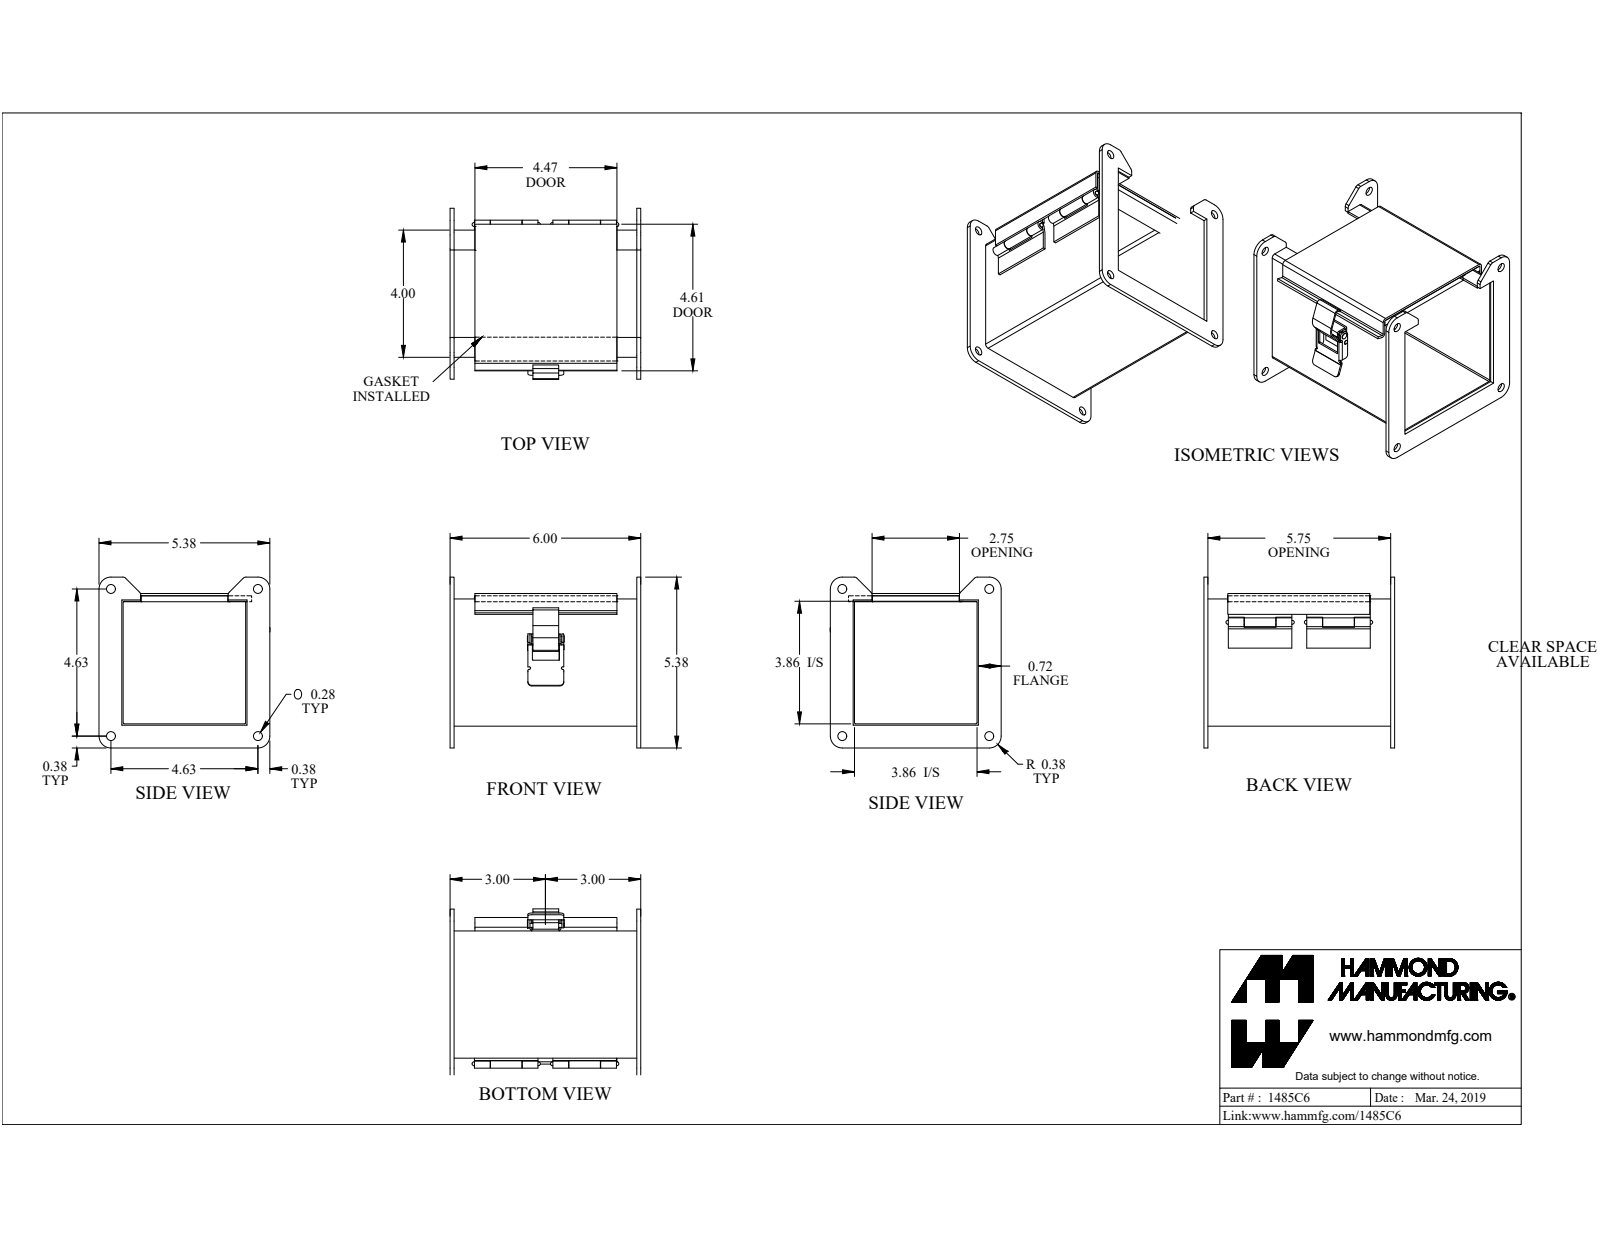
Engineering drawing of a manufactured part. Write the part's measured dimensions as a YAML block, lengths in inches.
part_name: "1485C6"
step_written_by: "SolidWorks 2019 (CONFIG_CONTROL_DESIGN)"
units: inches
bodies: {solids: 17, faces: 296, planar: 188, cylindrical: 104, other: 4}
overall_size: [6, 5.383, 5.375]
volume: 12.76
surface_area: 312.8
round_holes:
  - {diameter: 0.281, count: 4}
  - {diameter: 0.125, count: 1}
  - {diameter: 0.13, count: 1}
  - {diameter: 0.164, count: 1}
round_bosses_or_shafts:
  - {diameter: 0.187, count: 2}
  - {diameter: 0.275, count: 1}
  - {diameter: 0.156, count: 1}
  - {diameter: 0.125, count: 1}
partial_cylinders:
  - {radius: 0.016, count: 7}
  - {radius: 0.036, count: 7}
  - {radius: 0.108, count: 7}
  - {radius: 0.125, count: 7}
  - {radius: 0.375, count: 4}
  - {radius: 0.035, count: 3}
  - {radius: 0.039, count: 3}
  - {radius: 0.076, count: 3}
face_to_face_distances: [0.072, 3.928, 4.1, 4, 3.856, 4.028, 0.125, 5.875, 4.172, 0.172]
hole_center_spacings: [4.625, 6.541, 0.285, 1.054, 1.57, 1.849, 2.785, 3.057]
